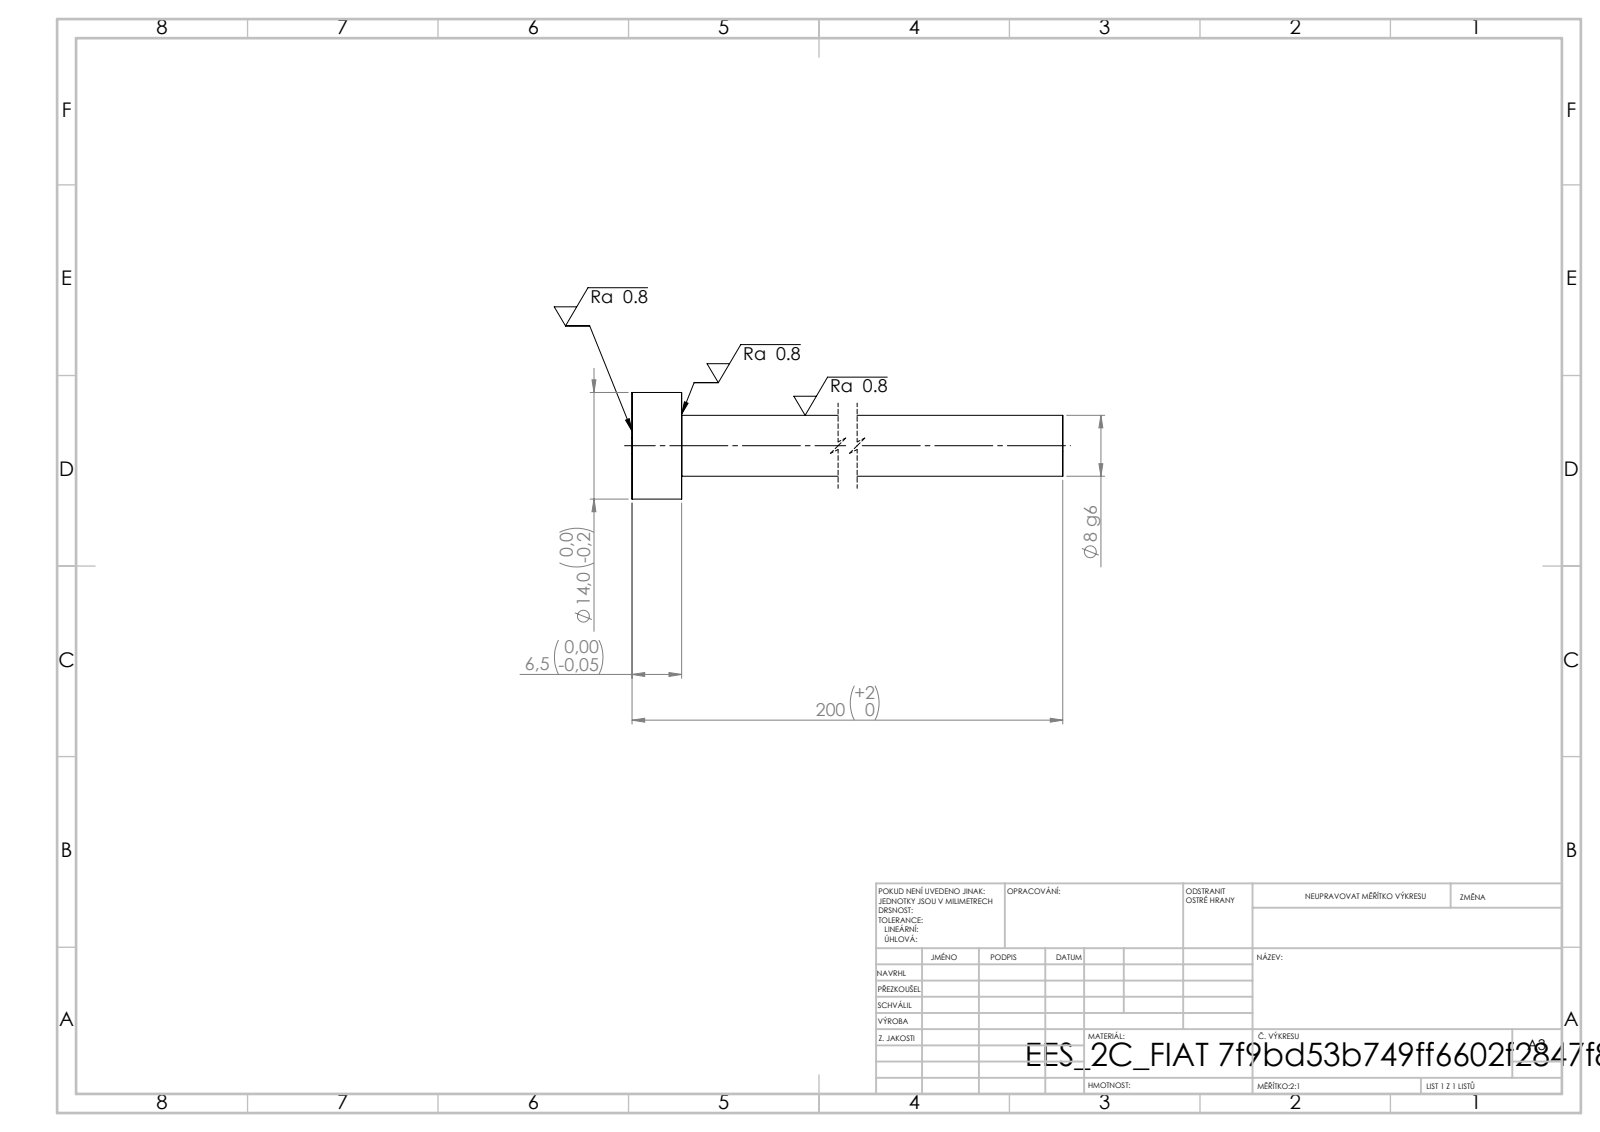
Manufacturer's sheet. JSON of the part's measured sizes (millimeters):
{"step_written_by": "SolidWorks 2019 (CONFIG_CONTROL_DESIGN)", "units": "millimeters", "bodies": {"solids": 1, "faces": 7, "planar": 3, "cylindrical": 4, "other": 0}, "overall_size": [200, 14, 14], "volume_mm3": 10727, "surface_area_mm2": 5457, "round_bosses_or_shafts": [[14, 1], [8, 1]], "face_to_face_distances": [6.5, 200, 193.5]}
